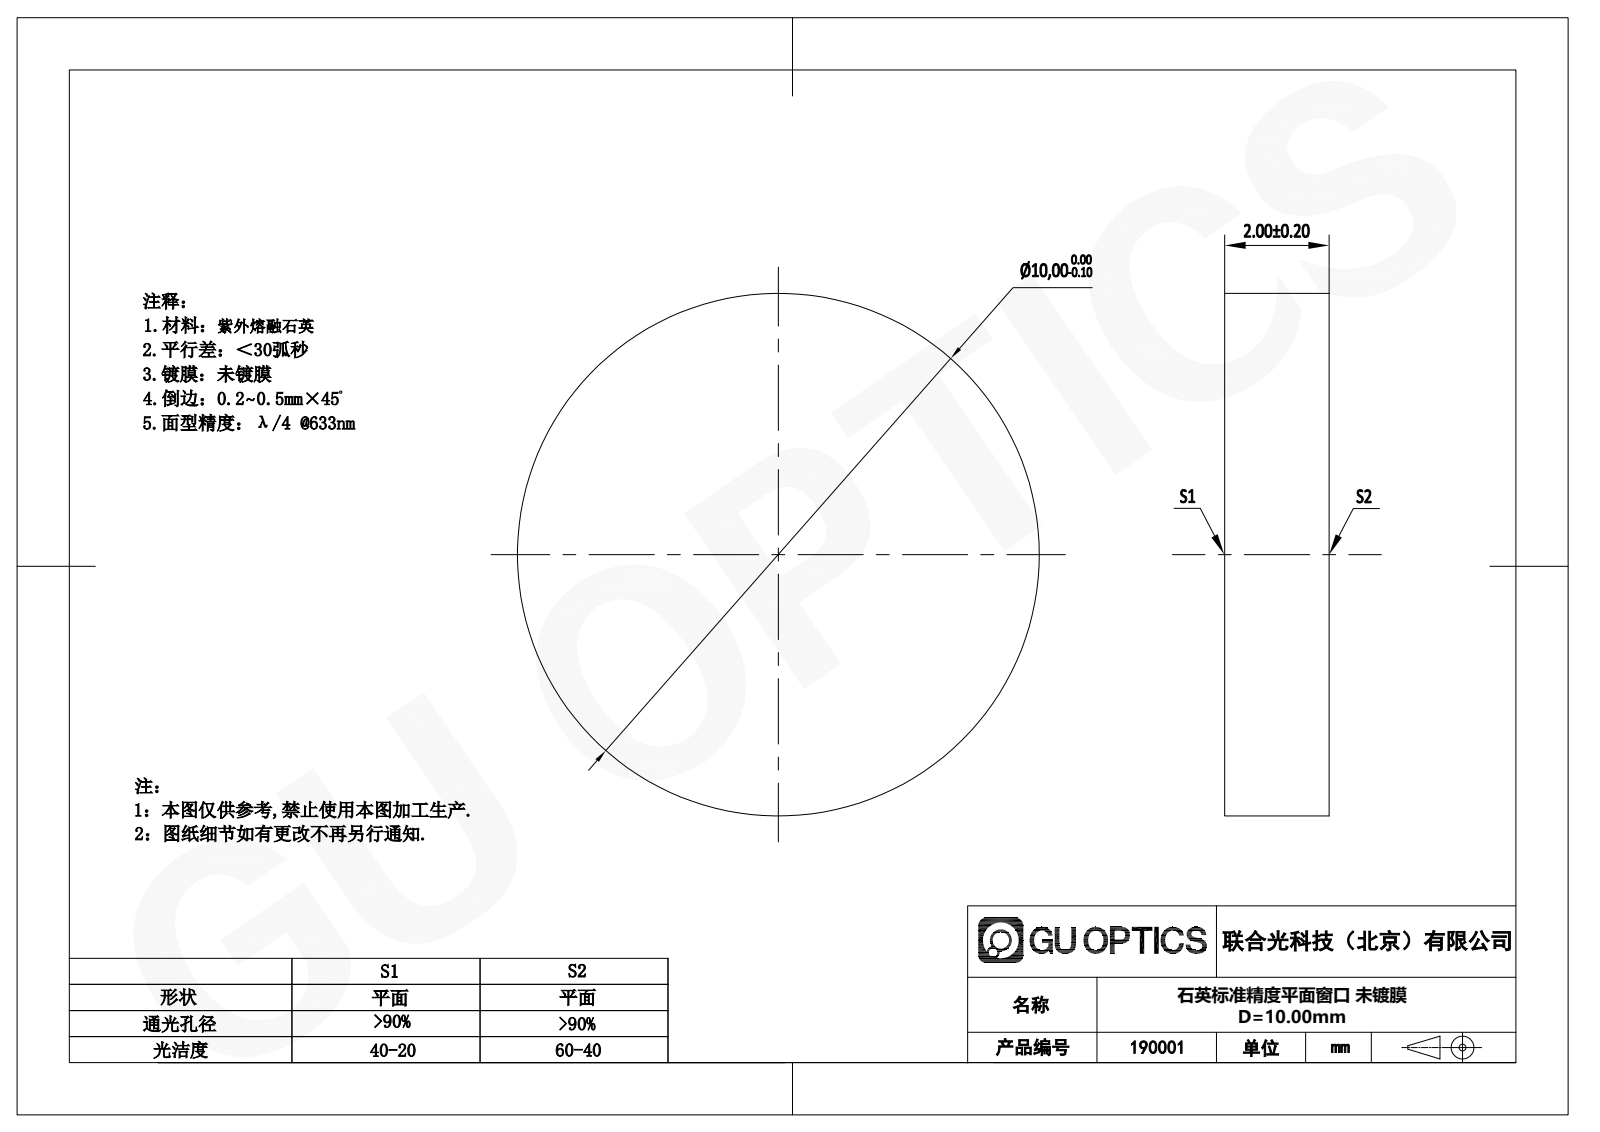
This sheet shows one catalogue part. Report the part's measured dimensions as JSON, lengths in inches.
{"part_name": "180001", "step_written_by": "SolidWorks 2016 (AUTOMOTIVE_DESIGN)", "units": "inches", "bodies": {"solids": 1, "faces": 4, "planar": 2, "cylindrical": 2, "other": 0}, "overall_size": [0.394, 0.394, 0.079], "volume_in3": 0.01, "surface_area_in2": 0.341, "round_bosses_or_shafts": [[0.394, 1]], "face_to_face_distances": [0.079]}
